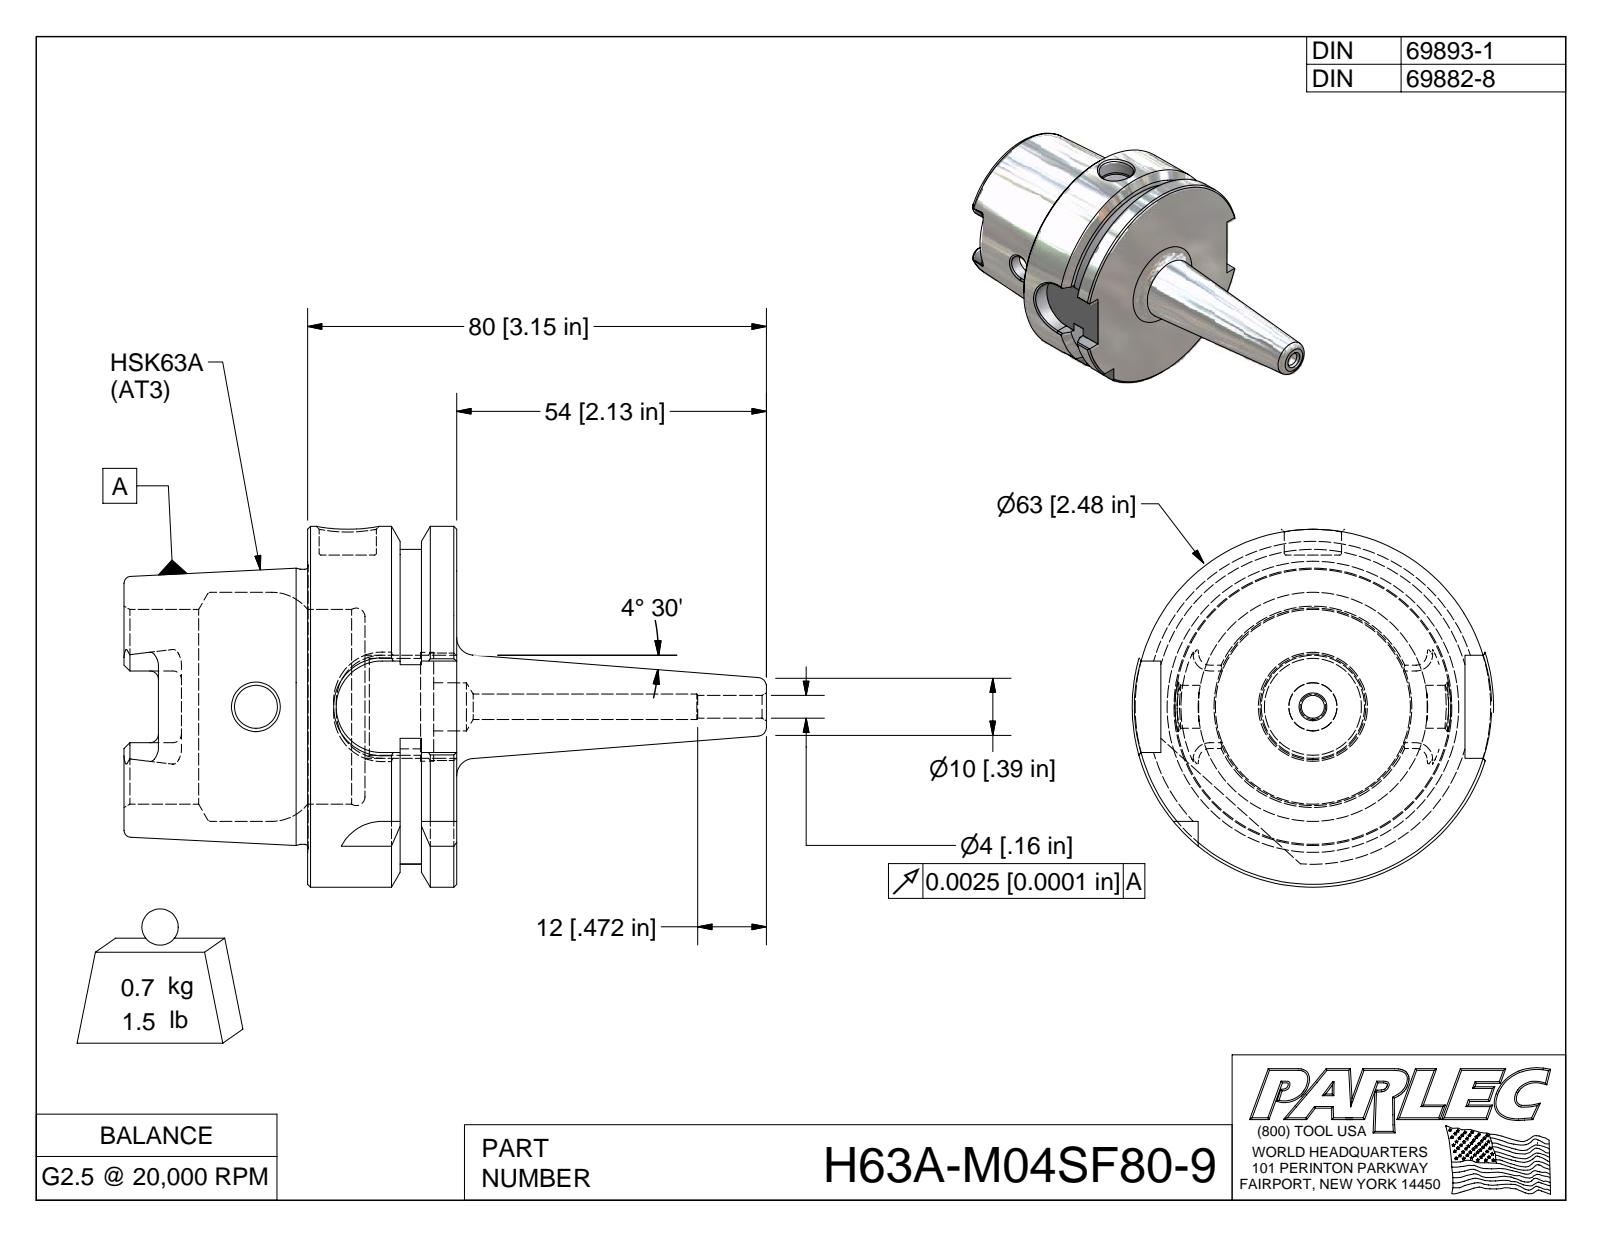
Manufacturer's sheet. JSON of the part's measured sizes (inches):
{"part_name": "H63A-M04SF80-9; H63A-M04SF80-9-1", "step_written_by": "Autodesk Inventor 2009 (AUTOMOTIVE_DESIGN)", "units": "inches", "bodies": {"solids": 1, "faces": 137, "planar": 48, "cylindrical": 33, "other": 56}, "overall_size": [4.409, 2.48, 2.48], "volume_in3": 5.438, "surface_area_in2": 39.52, "round_holes": [[0.157, 1], [0.295, 1], [0.331, 1], [0.394, 1], [0.666, 1], [0.749, 1], [1.339, 1], [1.575, 1]], "round_bosses_or_shafts": [[2.48, 1], [1.891, 1]], "partial_cylinders_radius": [[0.059, 6], [0.113, 4], [0.315, 4], [1.083, 1]], "face_to_face_distances": [1.024, 0.241, 0.389, 0.394, 0.63, 1.26, 2.283, 1.654, 1.894, 0.635]}
